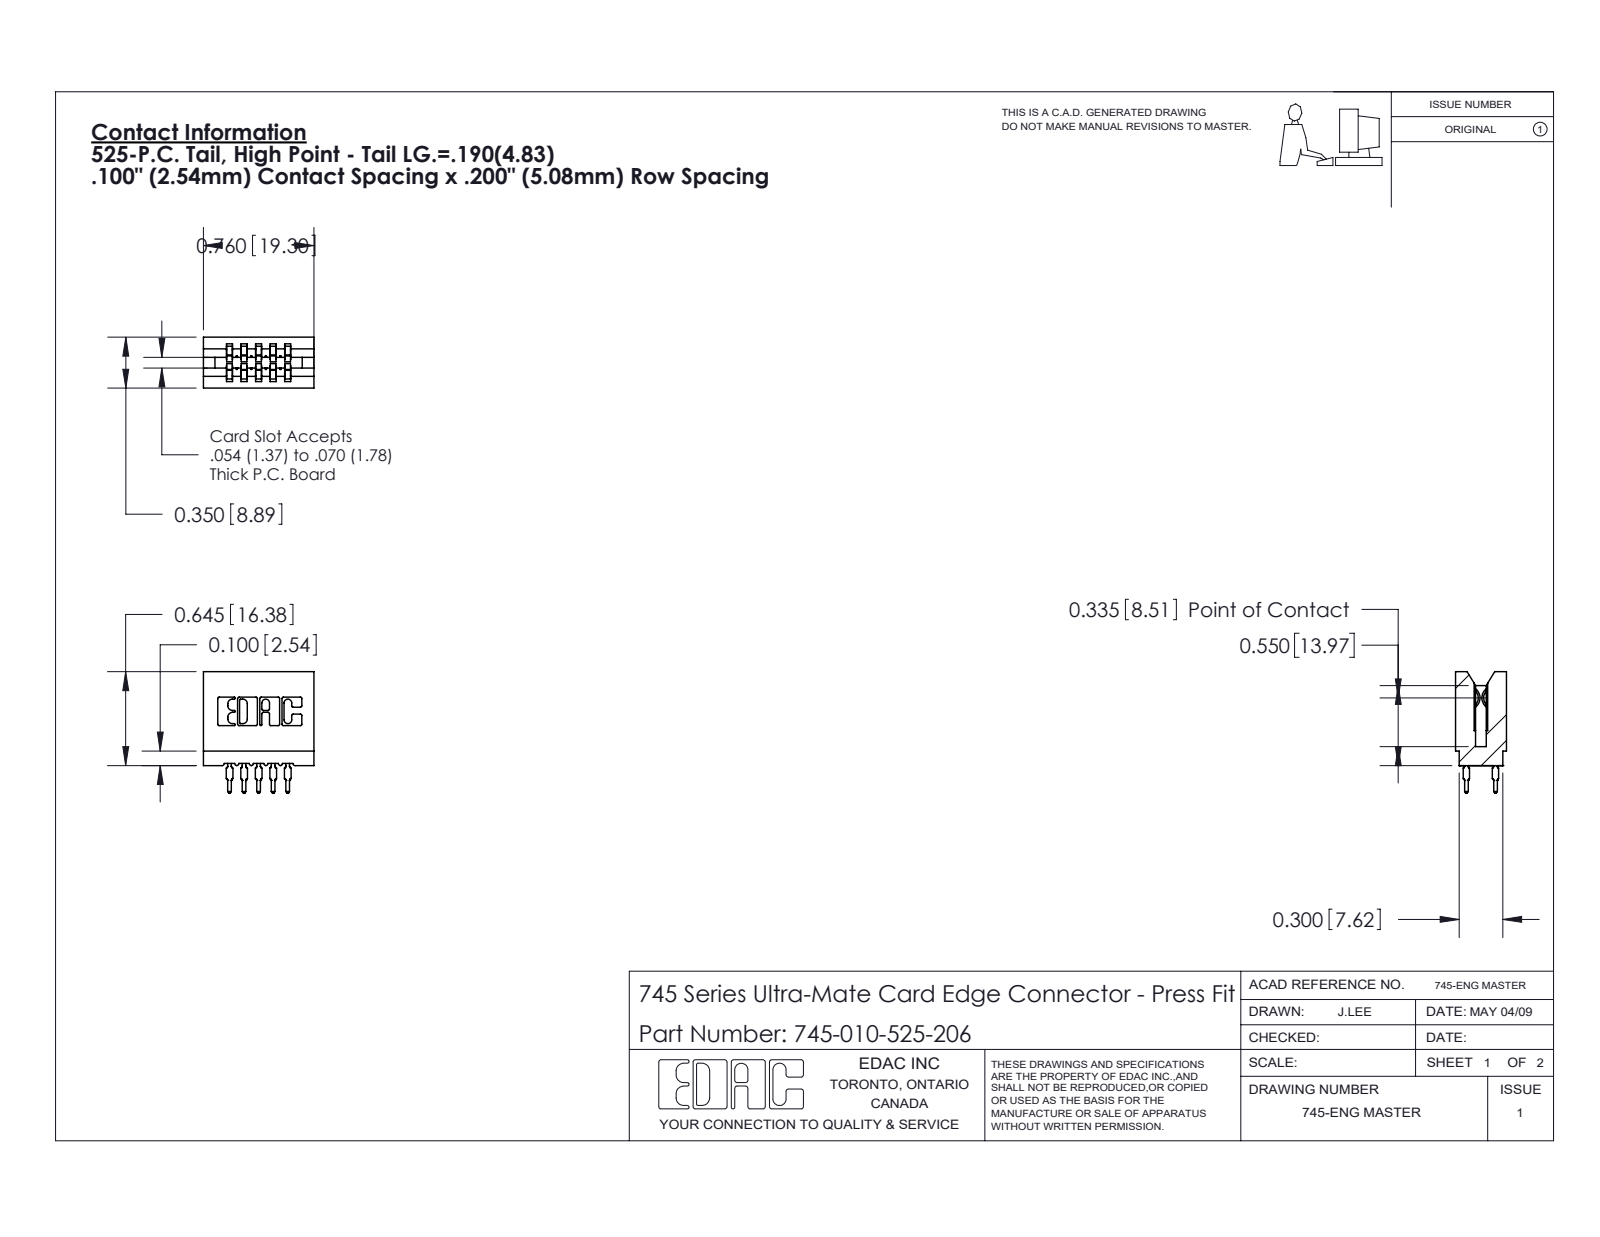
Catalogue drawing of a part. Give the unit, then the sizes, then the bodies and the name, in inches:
Units: inches
Overall size (bounding box): 0.836 × 0.76 × 0.35
Partial cylindrical surfaces — rounded edges, fillets, slot ends (radius × count): R0.01 ×22, R0.021 ×20, R0.015 ×10, R0.005 ×8, R0.011 ×8, R0.007 ×6, R0.031 ×6, R0.026 ×3
Main face-to-face distances: 0.1, 0.2, 0.042, 0.142, 0.3, 0.058, 0.35, 0.242, 0.158, 0.138
Volume: 0.118 in³ · Surface area: 4.803 in²
Bodies: 11 solids, 991 faces (516 planar, 215 cylindrical, 260 other)
Part name (STEP PRODUCT): 745 Part_Insulator Option - 06; 745-292-001_525; 745-010-525-206
STEP written by: SolidWorks 2020 (CONFIG_CONTROL_DESIGN)
